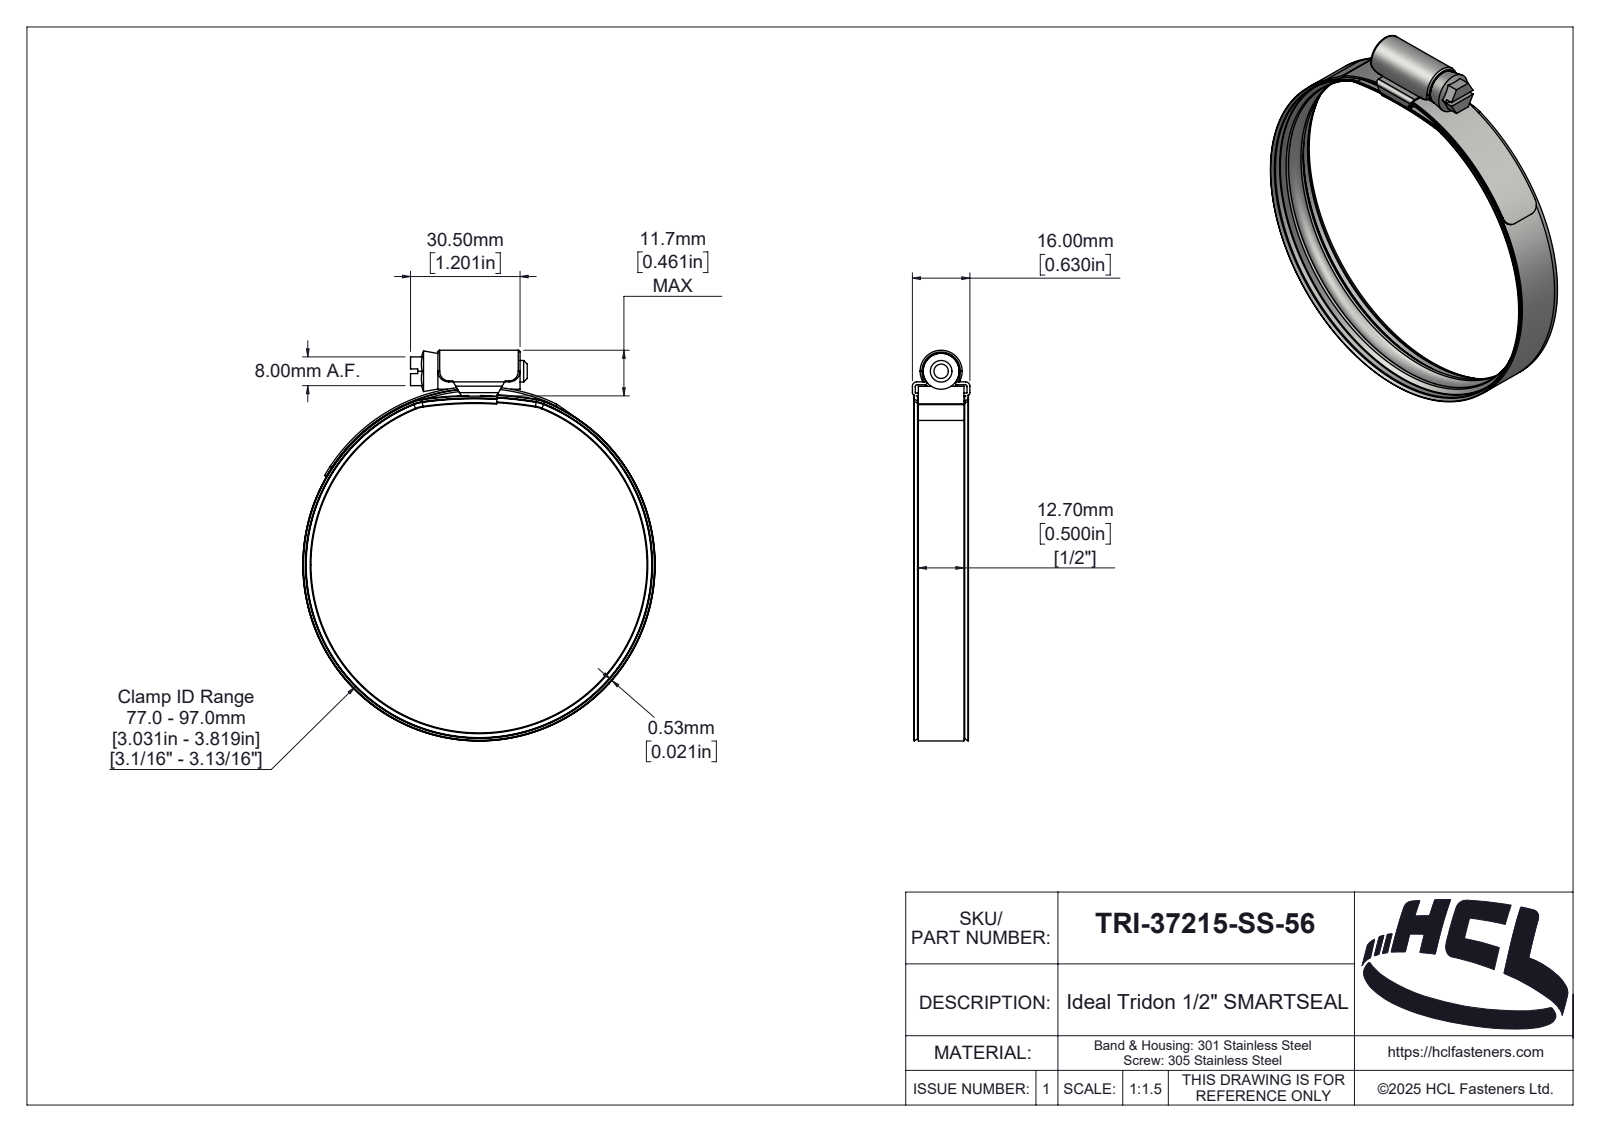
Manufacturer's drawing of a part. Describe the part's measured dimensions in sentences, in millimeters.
The part is named "TRI-37215-SS-56". Its 3-D file was written by "SolidWorks 2025 (AUTOMOTIVE_DESIGN)". It is 4 solids with 418 faces: 42 planar, 119 cylindrical and 257 other. Overall it measures 108.73 by 98.06 by 16 millimeters. Its volume is 6 518 cubic millimeters and its surface area 23 087 square millimeters. Round holes: 1 of diameter 96.4, 1 of diameter 97. Round bosses or shafts: 1 of diameter 98.06, 1 of diameter 96.8, 1 of diameter 10, 1 of diameter 6. Partial cylindrical surfaces (rounded edges, fillets, slot ends): 6 of radius 0.5, 4 of radius 3, 2 of radius 0.1, 2 of radius 0.9, 2 of radius 1.2, 2 of radius 9.9, 2 of radius 10.1, 1 of radius 0.46. The main face-to-face distances are 0.8, 12.7, 3.1, 0.53, 2.3, 30.5, 3.9, 1.65, 14.35, 15.2.
